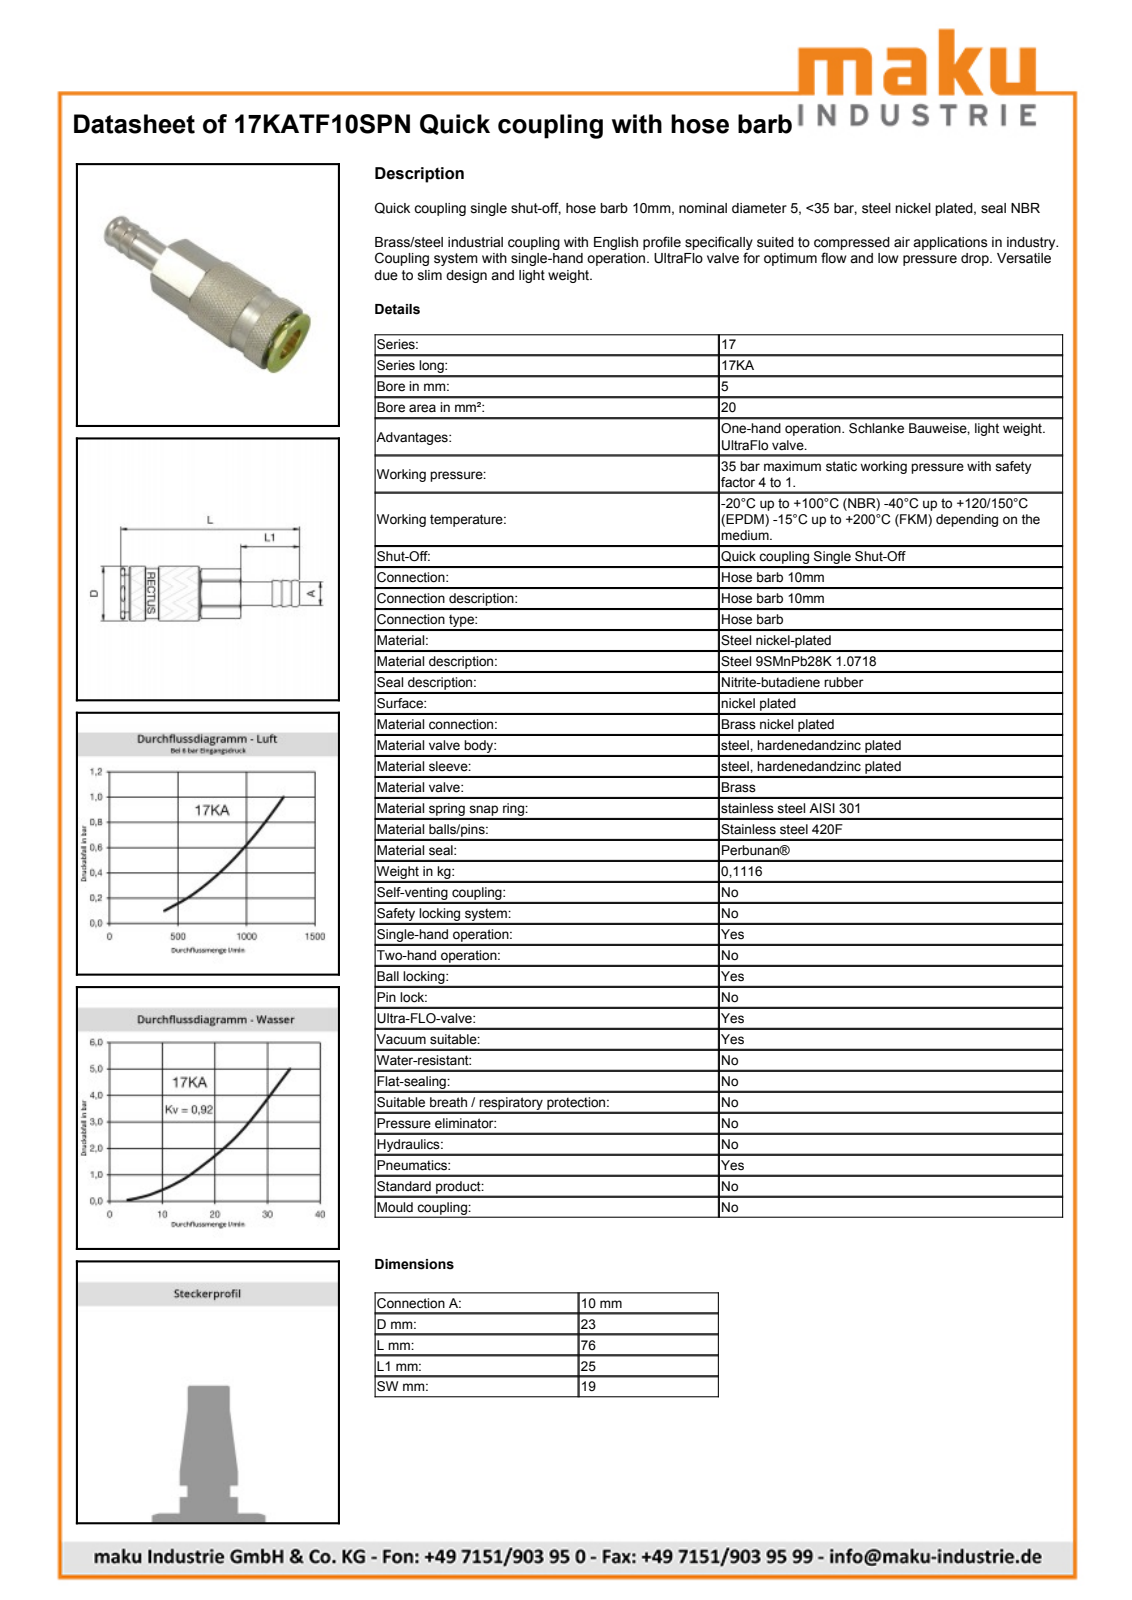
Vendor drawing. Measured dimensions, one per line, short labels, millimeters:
name: D107961
written by: Autodesk Inventor 2013 (AUTOMOTIVE_DESIGN)
unit: mm
bodies: 2 solids, 511 faces (212 planar, 58 cylindrical, 241 other)
size: 76.1 × 23.15 × 23.15
volume: 20 088 mm³; area: 8 965 mm²
holes: 1× ⌀16.15, 1× ⌀18.55, 1× ⌀19.25
bosses: 1× ⌀23.15, 1× ⌀21.5, 1× ⌀18.95, 1× ⌀16, 1× ⌀10.1
rounds: 1× R10.65, 1× R10.7, 1× R11
face distances: 19, 51.1, 3.65, 47.45, 1.8, 1.85, 49.3, 33.65, 31.85, 30
